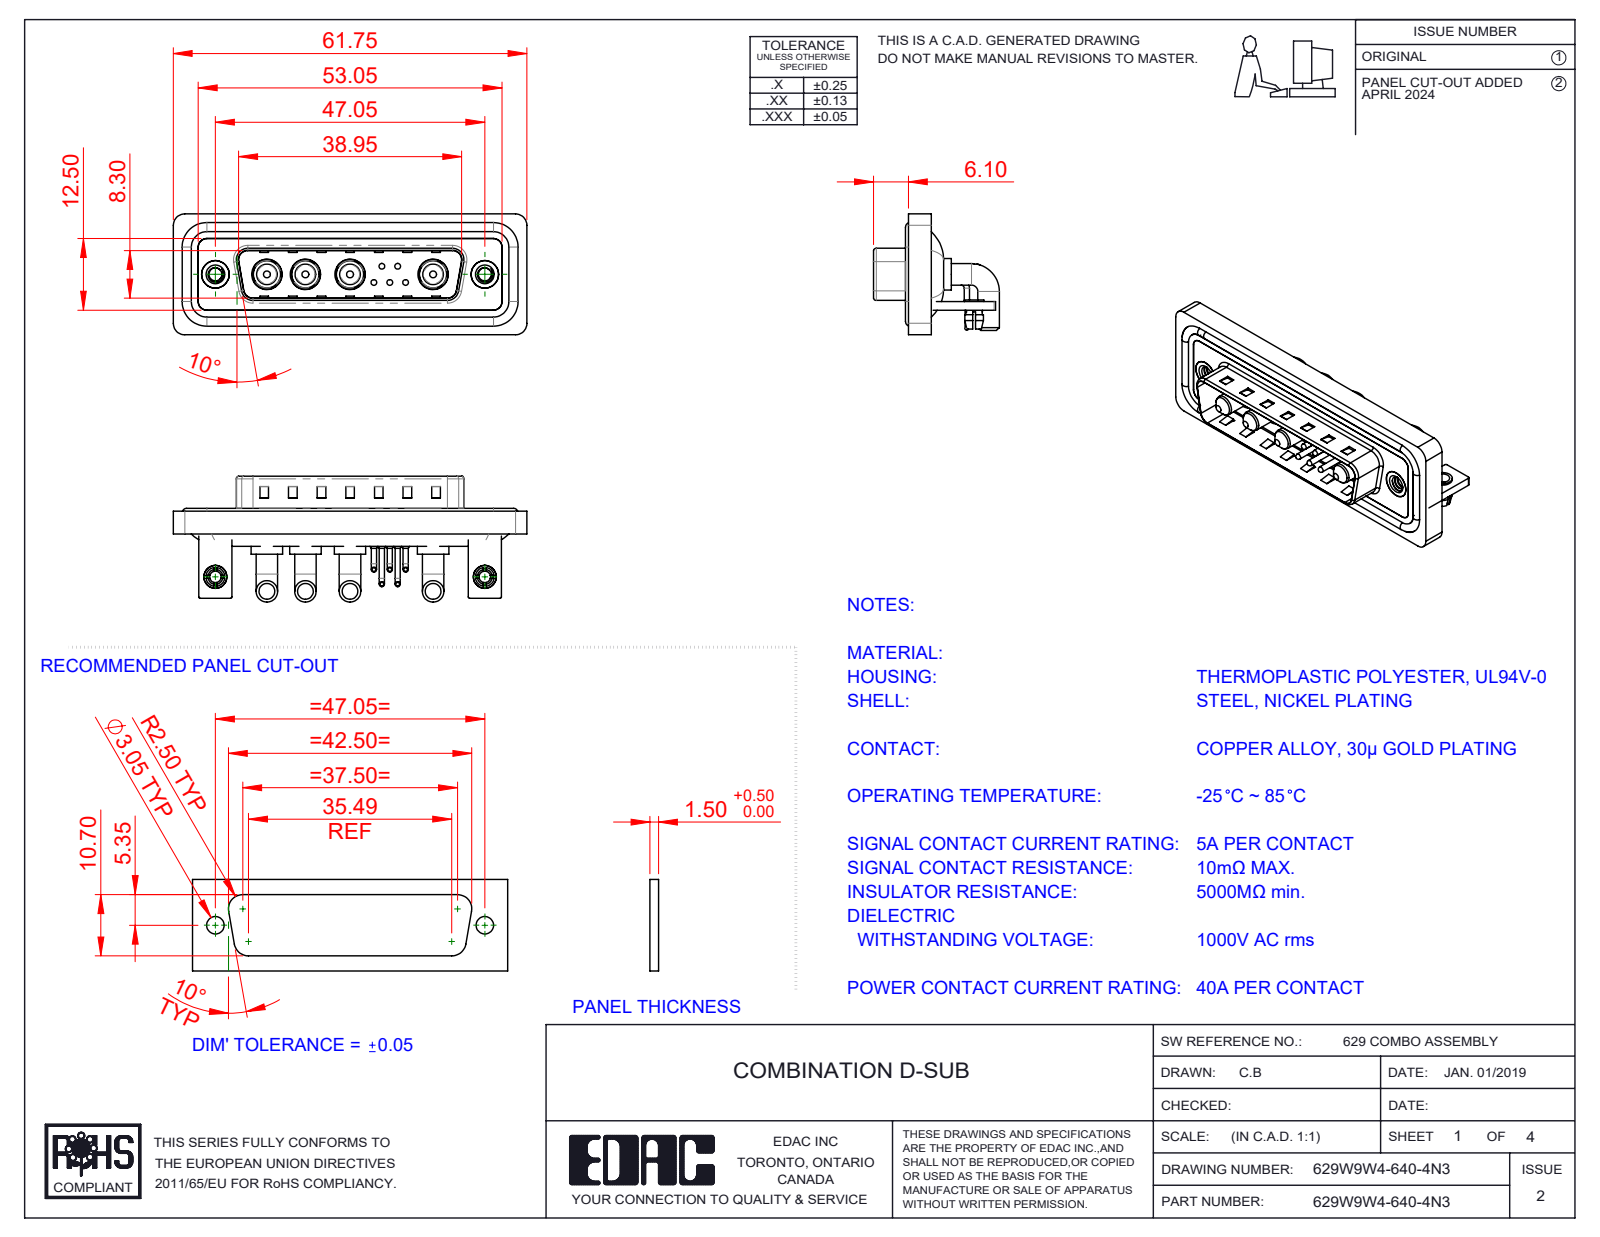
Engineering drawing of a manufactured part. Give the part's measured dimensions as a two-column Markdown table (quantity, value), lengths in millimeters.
| quantity | value |
| --- | --- |
| part name | 629Combo Board Lock; 629Combo Shell Rear_25 Contacts; 629Combo Contact Row 2; Power Pin_40A RA (+7 more) |
| STEP written by | SolidWorks 2023 (CONFIG_CONTROL_DESIGN) |
| units | millimeters |
| bodies | 24 solids, 1337 faces (637 planar, 502 cylindrical, 198 other) |
| overall size | 61.75 × 21.98 × 21.1 |
| volume | 8 310 mm³ |
| surface area | 13 349 mm² |
| round holes (diameter × count) | 2 × 7, 0.75 × 5, 1.6 × 5, 4.85 × 4, 5.3 × 4, 2.26 × 2, 2.5 × 2, 3.2 × 2, 4 × 2, 4.8 × 2, 5 × 2 |
| round bosses / shafts (diameter × count) | 0.9 × 10, 3.75 × 8, 1.5 × 5, 1 × 5, 0.65 × 5, 5.5 × 4, 5.2 × 4, 4.75 × 4 |
| partial cylindrical surfaces (radius × count) | 2 × 19, 1.5 × 18, 0.25 × 16, 0.5 × 9, 1.6 × 8, 1.01 × 5, 0.6 × 4, 0.65 × 4 |
| main face-to-face distances | 0.4, 1.5, 0.8, 2.9, 2.1, 1.1, 3.7, 4.1, 4.5, 1.6 |
| hole center spacings | 3.16, 2.77, 5.04, 14.5, 47.05, 2.78, 4.4, 4.41 |
